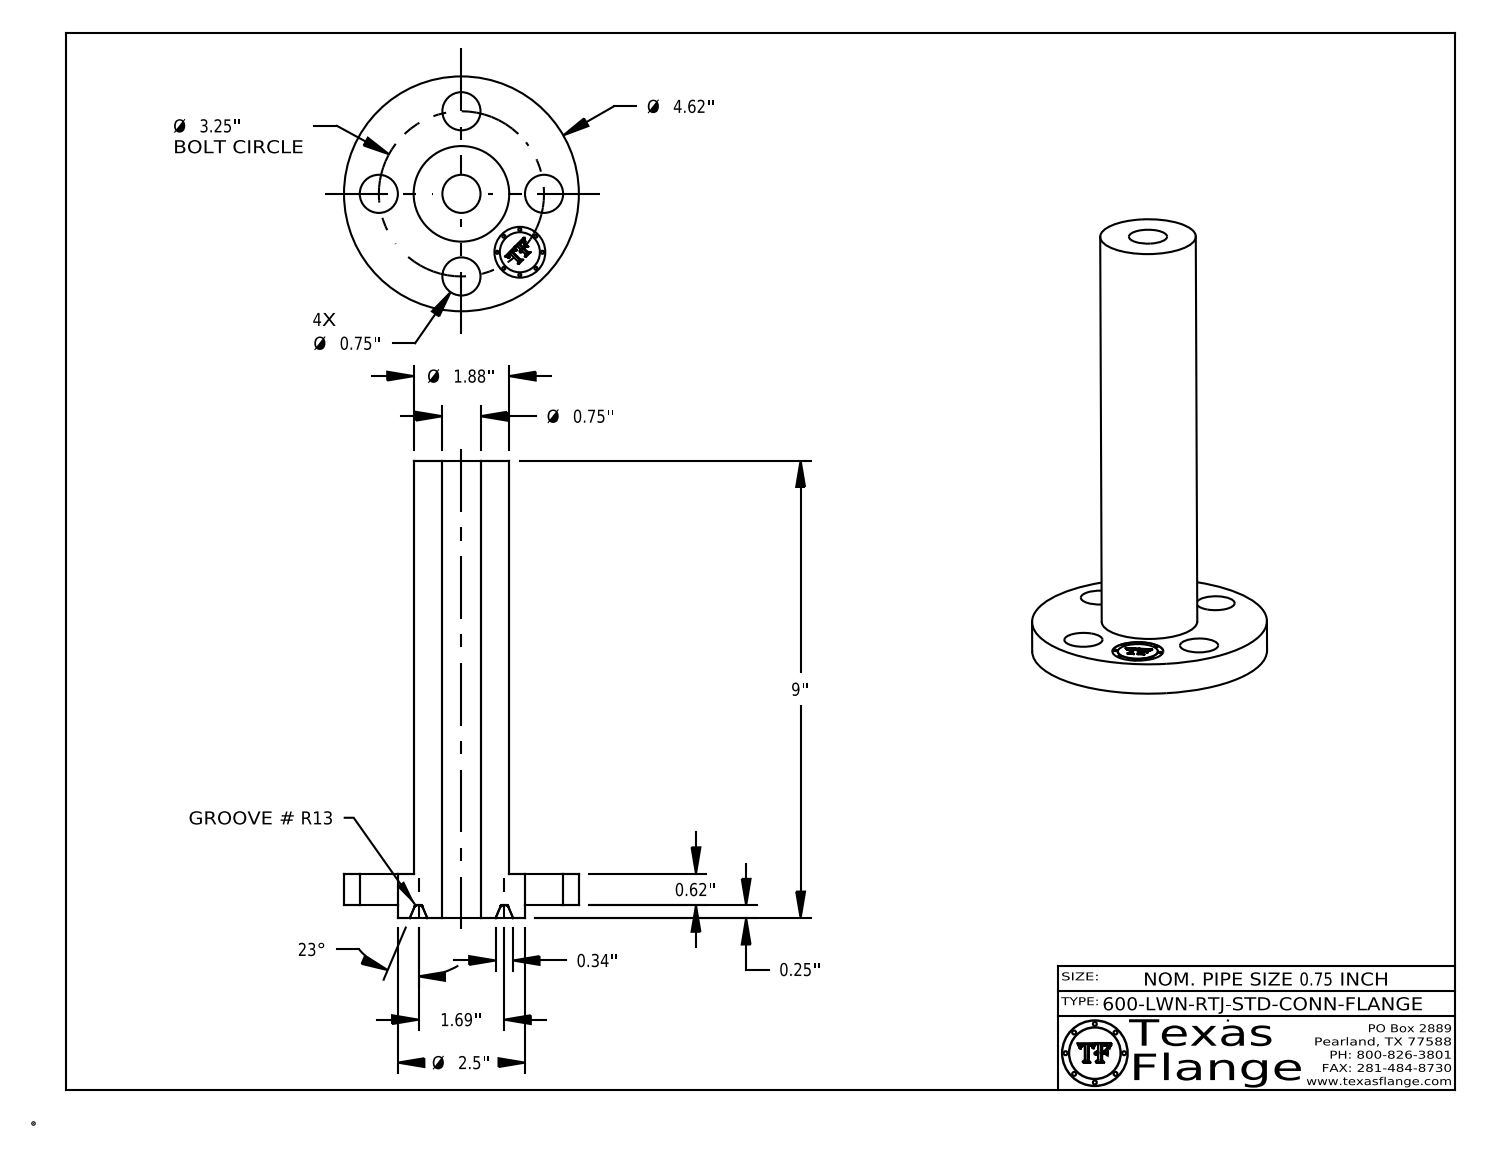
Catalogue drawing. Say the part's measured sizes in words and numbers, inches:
The part is named "0.75-600-LWN-RTJ-STD-CONN-FLANGE". Its 3-D file was written by "CATIA V5 STEP AP214 (AUTOMOTIVE_DESIGN)". It is 1 solid with 415 faces: 371 planar, 36 cylindrical and 8 other. Overall it measures 9 by 4.62 by 4.62 inches. Its volume is 28.8 cubic inches and its surface area 116.9 square inches. Round holes: 5 of diameter 0.75, 1 of diameter 1. Round bosses or shafts: 8 of diameter 0.061, 1 of diameter 4.62, 1 of diameter 2.5, 1 of diameter 1.88, 1 of diameter 0.788. The main face-to-face distances are 0.62, 0.25, 0.87, 9, 8.75, 8.13, 0.865, 0.615, 8.135, 0.298. The hole center spacings are 1.625, 2.298, 1.244, 3.003, 3.25.
